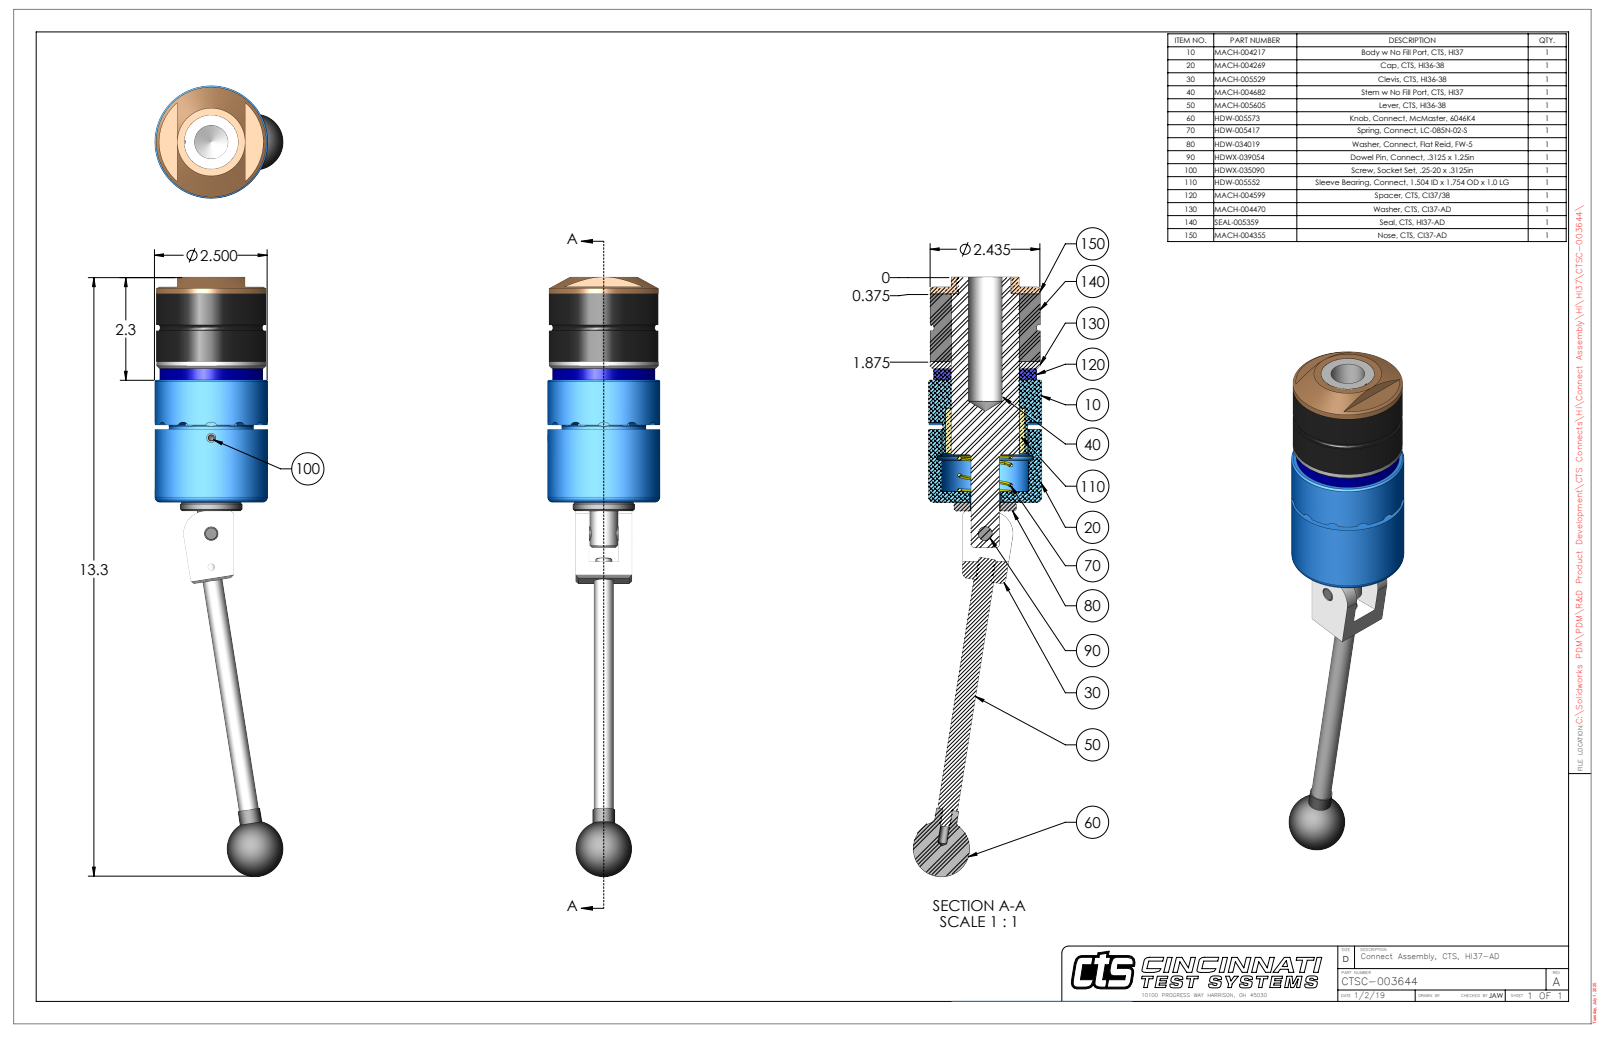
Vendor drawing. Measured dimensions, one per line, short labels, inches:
name: CTSC-003644
written by: SolidWorks 2023 (AUTOMOTIVE_DESIGN)
unit: in
bodies: 11 solids, 279 faces (97 planar, 110 cylindrical, 72 other)
size: 13.275 × 2.843 × 2.5
volume: 25.39 in³; area: 137 in²
holes: 2× ⌀0.201, 1× ⌀0.15, 1× ⌀0.311, 1× ⌀0.313, 1× ⌀0.314, 1× ⌀0.656, 1× ⌀0.696, 1× ⌀0.75, 1× ⌀1.172, 1× ⌀1.495, 1× ⌀1.501, 1× ⌀1.51
bosses: 1× ⌀2.5, 1× ⌀2.435, 1× ⌀2.435, 1× ⌀2.281, 1× ⌀1.875, 1× ⌀1.5, 1× ⌀1.496, 1× ⌀1.38
rounds: 12× R0.12, 2× R0.029, 1× R0.5, 1× R1.203
face distances: 1.5, 0.402, 1.902, 0.25, 2.713, 0.152, 1.652, 2.963, 3.115, 4.615
hole spacings: 0.74, 2.118, 2.858
